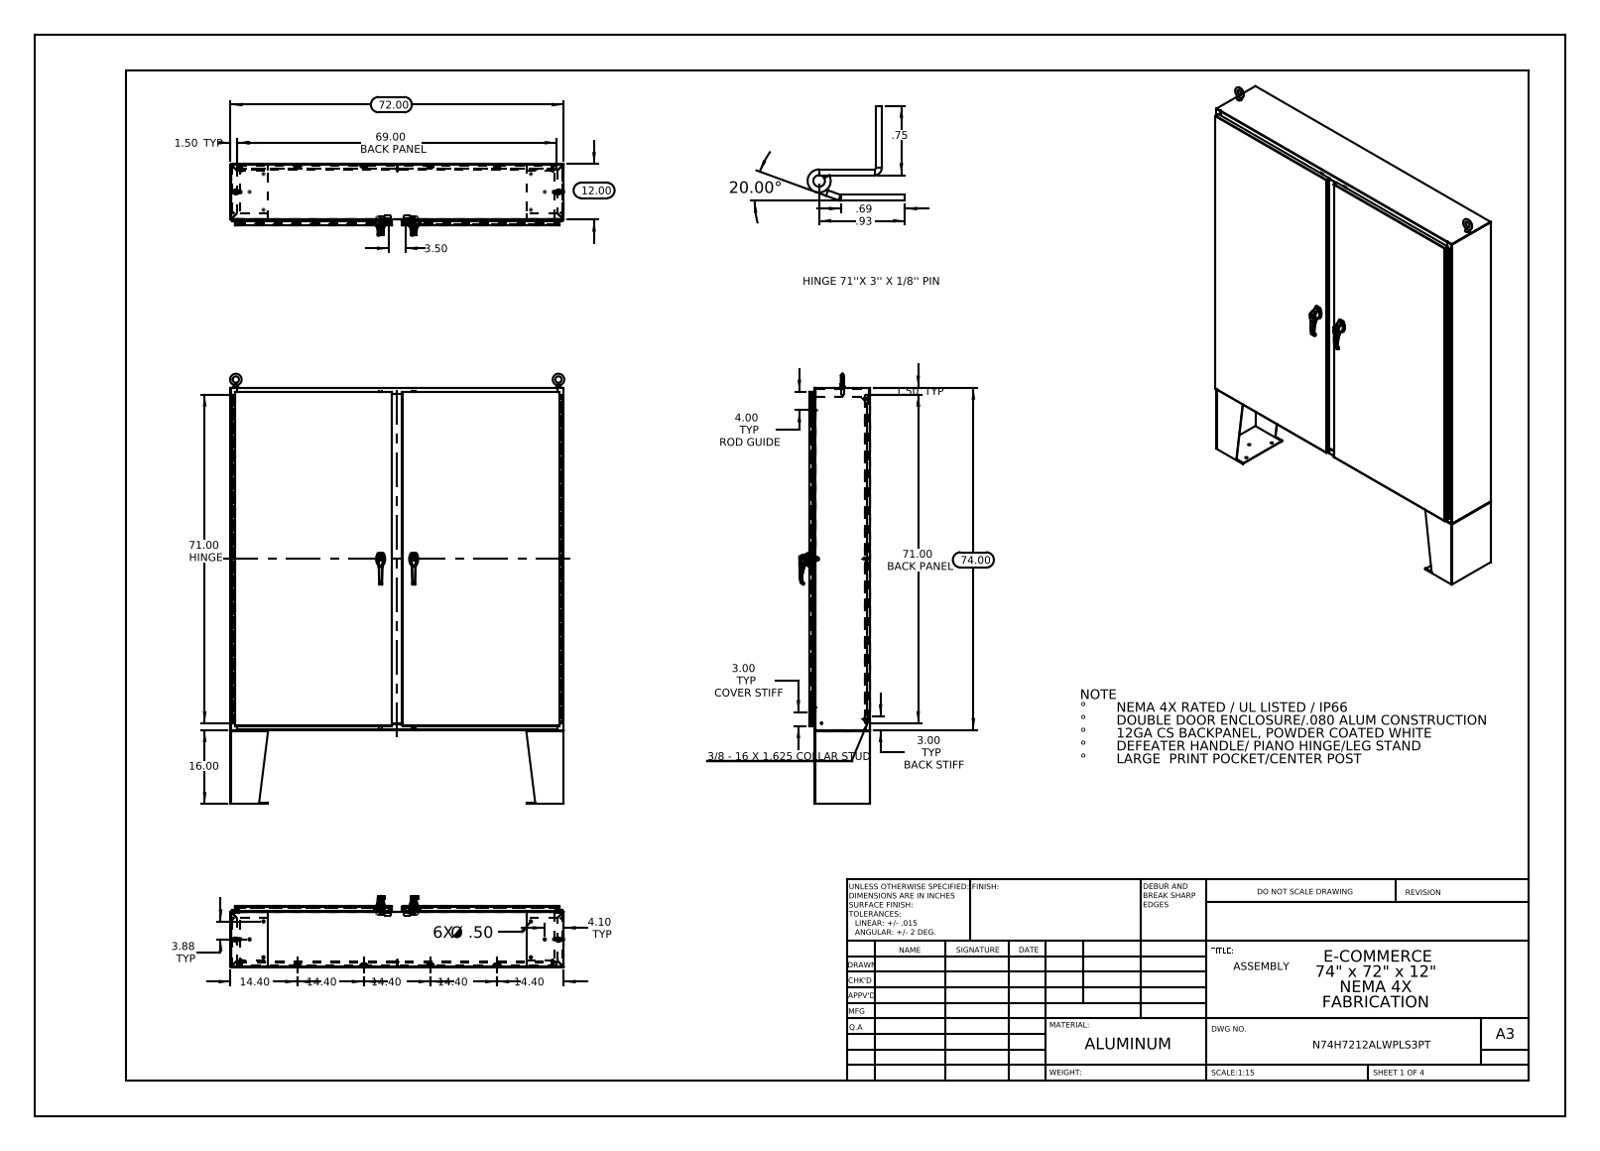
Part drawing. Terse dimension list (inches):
name: N74H7212SSWPLS3PT Backpanel; 26161102; 297025; NMP-SS-RODGUIDES_unfolded_DefaultSM-FLAT-PATTERN (+8 more)
written by: SolidWorks 2013 (CONFIG_CONTROL_DESIGN)
unit: in
bodies: 83 solids, 7630 faces (3104 planar, 3066 cylindrical, 1460 other)
size: 93 × 72.226 × 15.307
volume: 1 936 in³; area: 46 970 in²
holes: 20× ⌀0.25, 14× ⌀0.5, 6× ⌀0.138, 6× ⌀0.161, 4× ⌀0.079, 4× ⌀0.313, 4× ⌀0.437, 4× ⌀0.75, 2× ⌀0.125, 2× ⌀0.125, 2× ⌀0.197, 2× ⌀0.203
bosses: 12× ⌀0.157, 12× ⌀0.14, 10× ⌀0.625, 8× ⌀0.375, 8× ⌀0.33, 5× ⌀0.315, 5× ⌀0.236, 2× ⌀1.181
rounds: 72× R0.118, 66× R0.006, 50× R0.013, 42× R0.088, 28× R0.039, 24× R0.028, 12× R0.008, 12× R0.02
face distances: 0.075, 13.126, 0.104, 13.051, 1.075, 13.201, 1, 12.051, 12.126, 1.179
hole spacings: 7.152, 30.364, 0.295, 0.625, 0.841, 1.313, 1.561, 7.117
